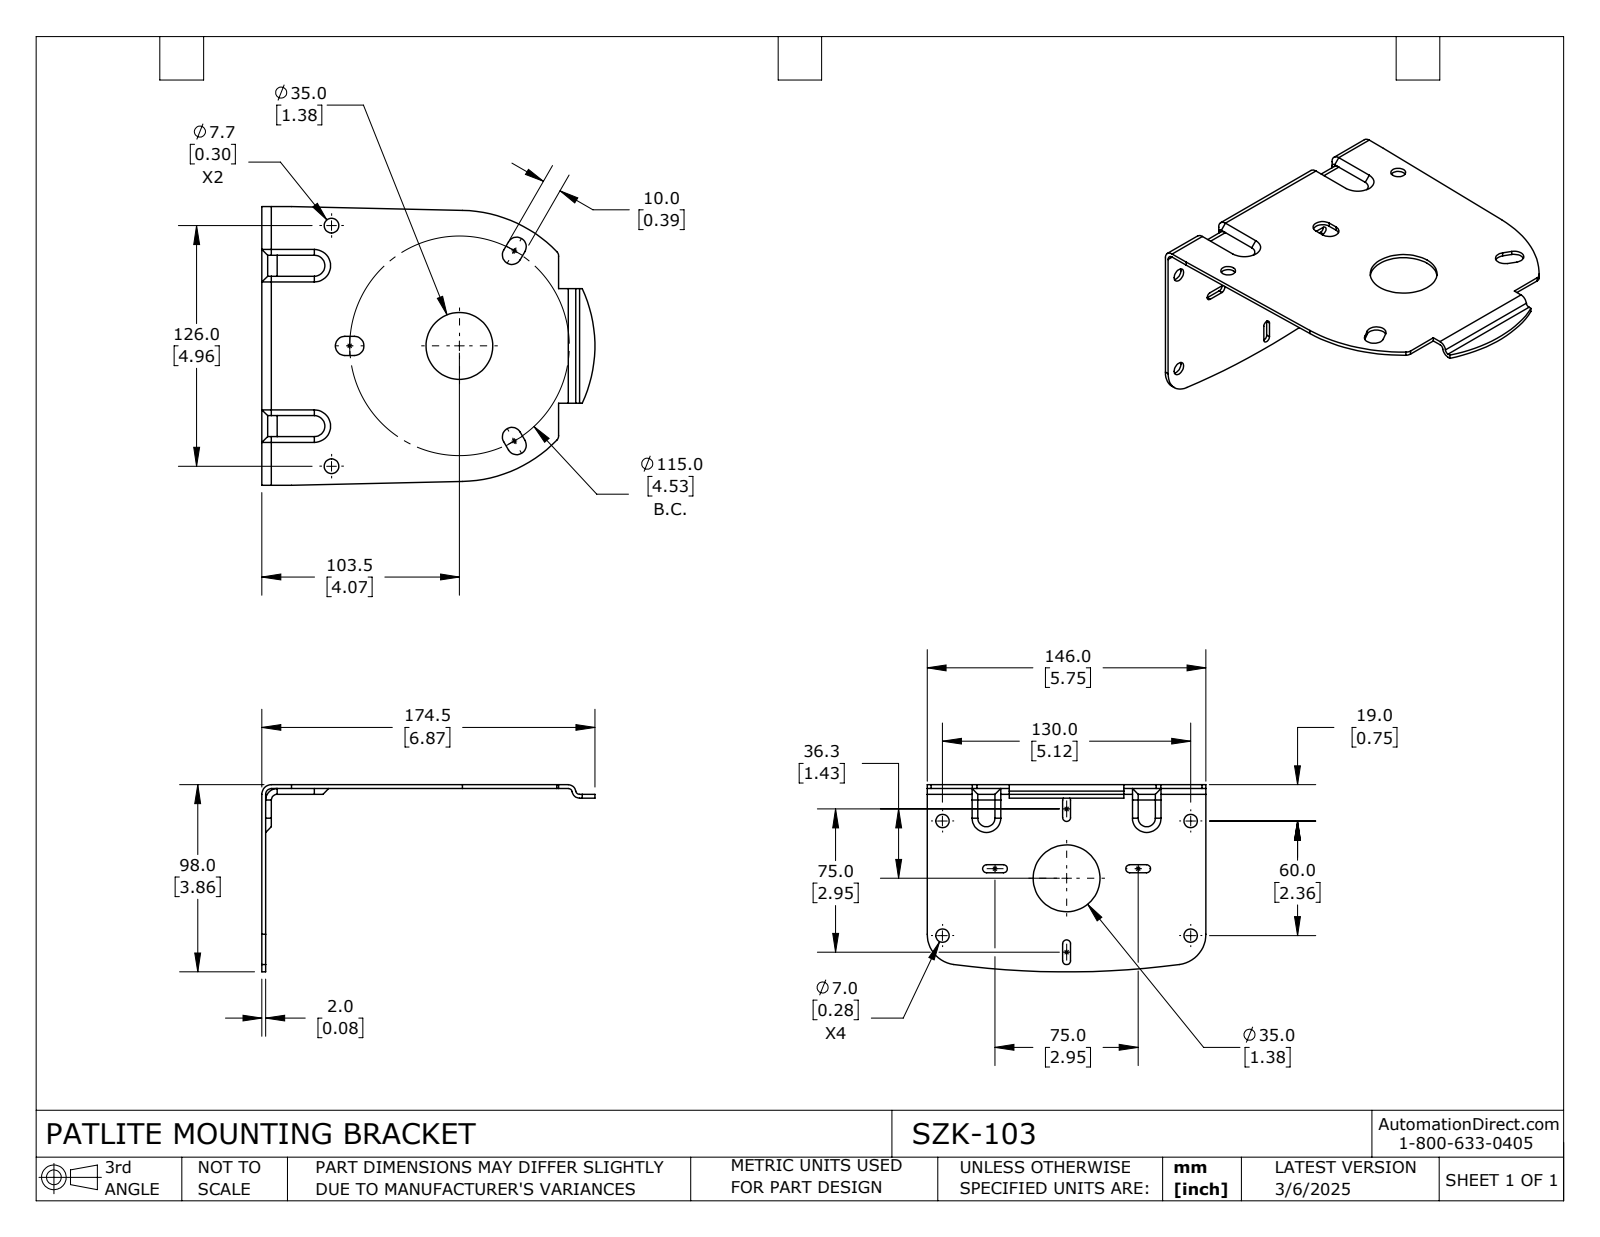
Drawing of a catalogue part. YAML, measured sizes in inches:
part_name: "SZK-103"
step_written_by: "SolidWorks 2024 (CONFIG_CONTROL_DESIGN)"
units: inches
bodies: {solids: 1, faces: 132, planar: 60, cylindrical: 56, other: 16}
overall_size: [6.87, 5.748, 3.858]
volume: 4.014
surface_area: 108.2
round_holes:
  - {diameter: 0.276, count: 4}
  - {diameter: 0.303, count: 2}
  - {diameter: 1.378, count: 2}
partial_cylinders:
  - {radius: 0.083, count: 8}
  - {radius: 0.197, count: 8}
  - {radius: 0.079, count: 2}
  - {radius: 0.118, count: 2}
  - {radius: 0.138, count: 2}
  - {radius: 0.157, count: 2}
  - {radius: 0.63, count: 2}
  - {radius: 2.795, count: 1}
face_to_face_distances: [0.079, 0.118, 0.197, 0.039, 2.338, 0.157, 0.276, 0.028, 2.31, 2.338]
hole_center_spacings: [2.819, 2.362, 3.621, 5.118, 5.637, 4.961]
